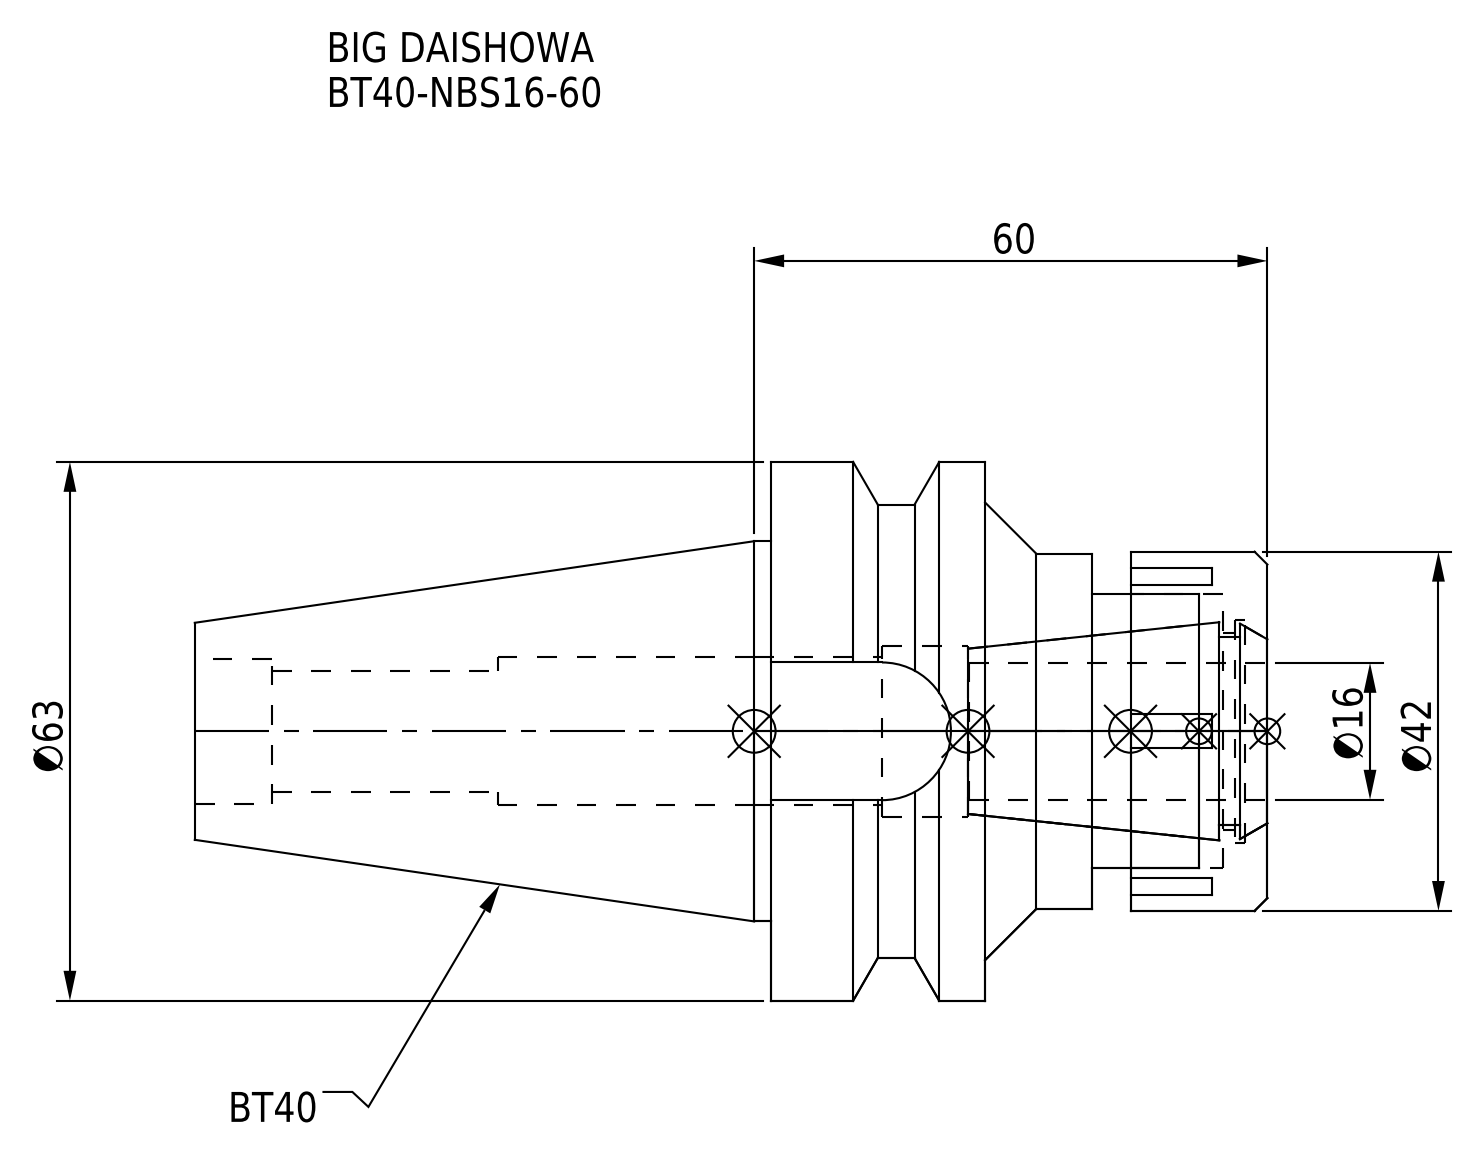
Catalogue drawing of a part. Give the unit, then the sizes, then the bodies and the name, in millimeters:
Units: millimetres
Overall size (bounding box): 125.4 × 63 × 63
Round holes (diameter × count): ⌀14.2 ×1, ⌀17 ×1, ⌀17.3 ×1, ⌀20 ×1, ⌀23 ×1, ⌀26 ×1, ⌀32 ×1
Round bosses / shafts (diameter × count): ⌀63 ×1, ⌀53 ×1, ⌀44.45 ×1, ⌀42 ×1, ⌀41.5 ×1
Partial cylindrical surfaces — rounded edges, fillets, slot ends (radius × count): R8.05 ×1
Main face-to-face distances: 25, 12.5, 33, 58, 8, 20.5, 37.5, 16, 4.5, 17
Volume: 143 884 mm³ · Surface area: 33 282 mm²
Bodies: 2 solids, 90 faces (44 planar, 32 cylindrical, 14 other)
Part name (STEP PRODUCT): BT40-NBS16-60.stp; BT40-NBS16-60_1.stp; BT40-NBS16-60; BT40NB16060-160_ASM.stp (+3 more)
STEP written by: SolidWorks 2019 (CONFIG_CONTROL_DESIGN)
